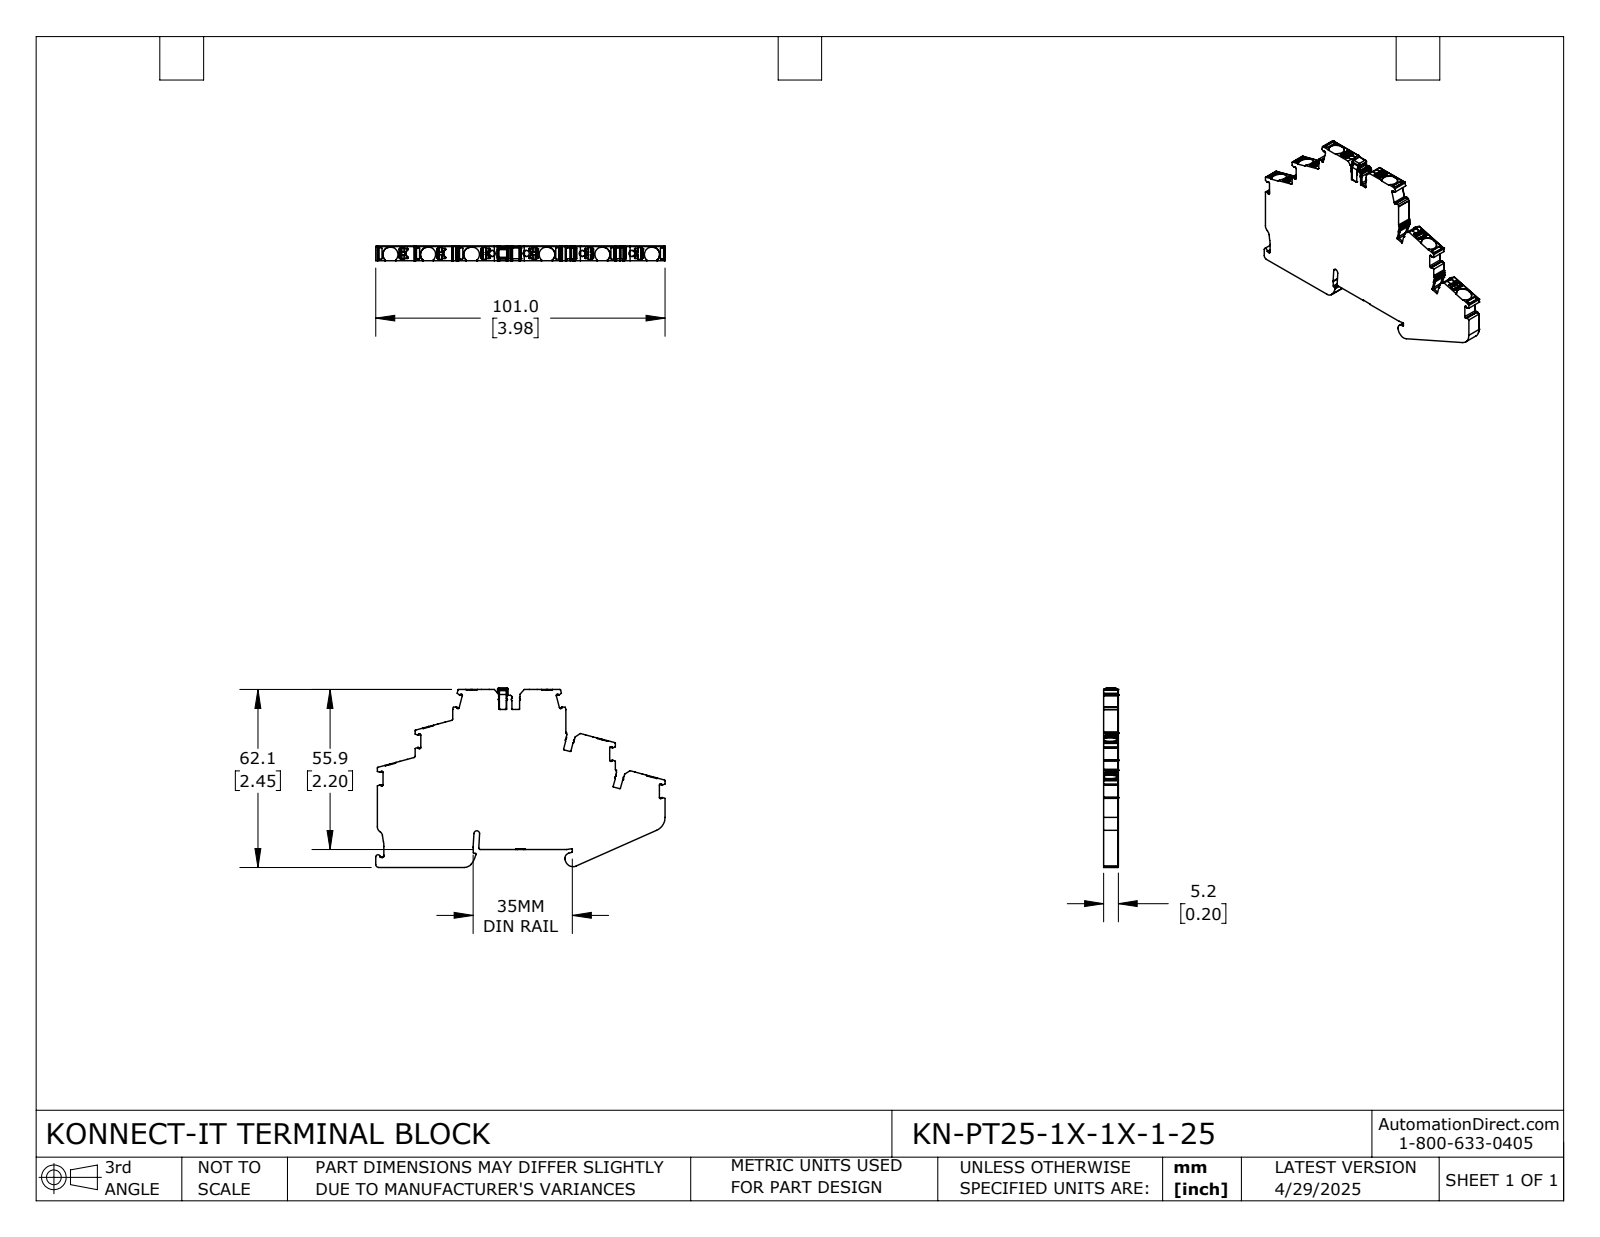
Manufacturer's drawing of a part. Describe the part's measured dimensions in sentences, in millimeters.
The part is named "KN-PT25-1X-1X-1-25". Its 3-D file was written by "SolidWorks 2024 (CONFIG_CONTROL_DESIGN)". It is 1 solid with 1314 faces: 638 planar, 565 cylindrical and 111 other. Overall it measures 101 by 62.7 by 5.2 millimeters. Its volume is 22 290 cubic millimeters and its surface area 10 910 square millimeters. Round holes: 4 of diameter 2.1. Partial cylindrical surfaces (rounded edges, fillets, slot ends): 132 of radius 0.2, 51 of radius 0.3, 49 of radius 0.1, 34 of radius 0.5, 24 of radius 0.2, 17 of radius 0.4, 14 of radius 0.6, 12 of radius 0.2. The main face-to-face distances are 5.2, 6.2, 2, 55.7, 61.9, 8.1, 17.3, 13.2, 55.9, 62.1. The hole center spacings are 11.8, 20.1.
